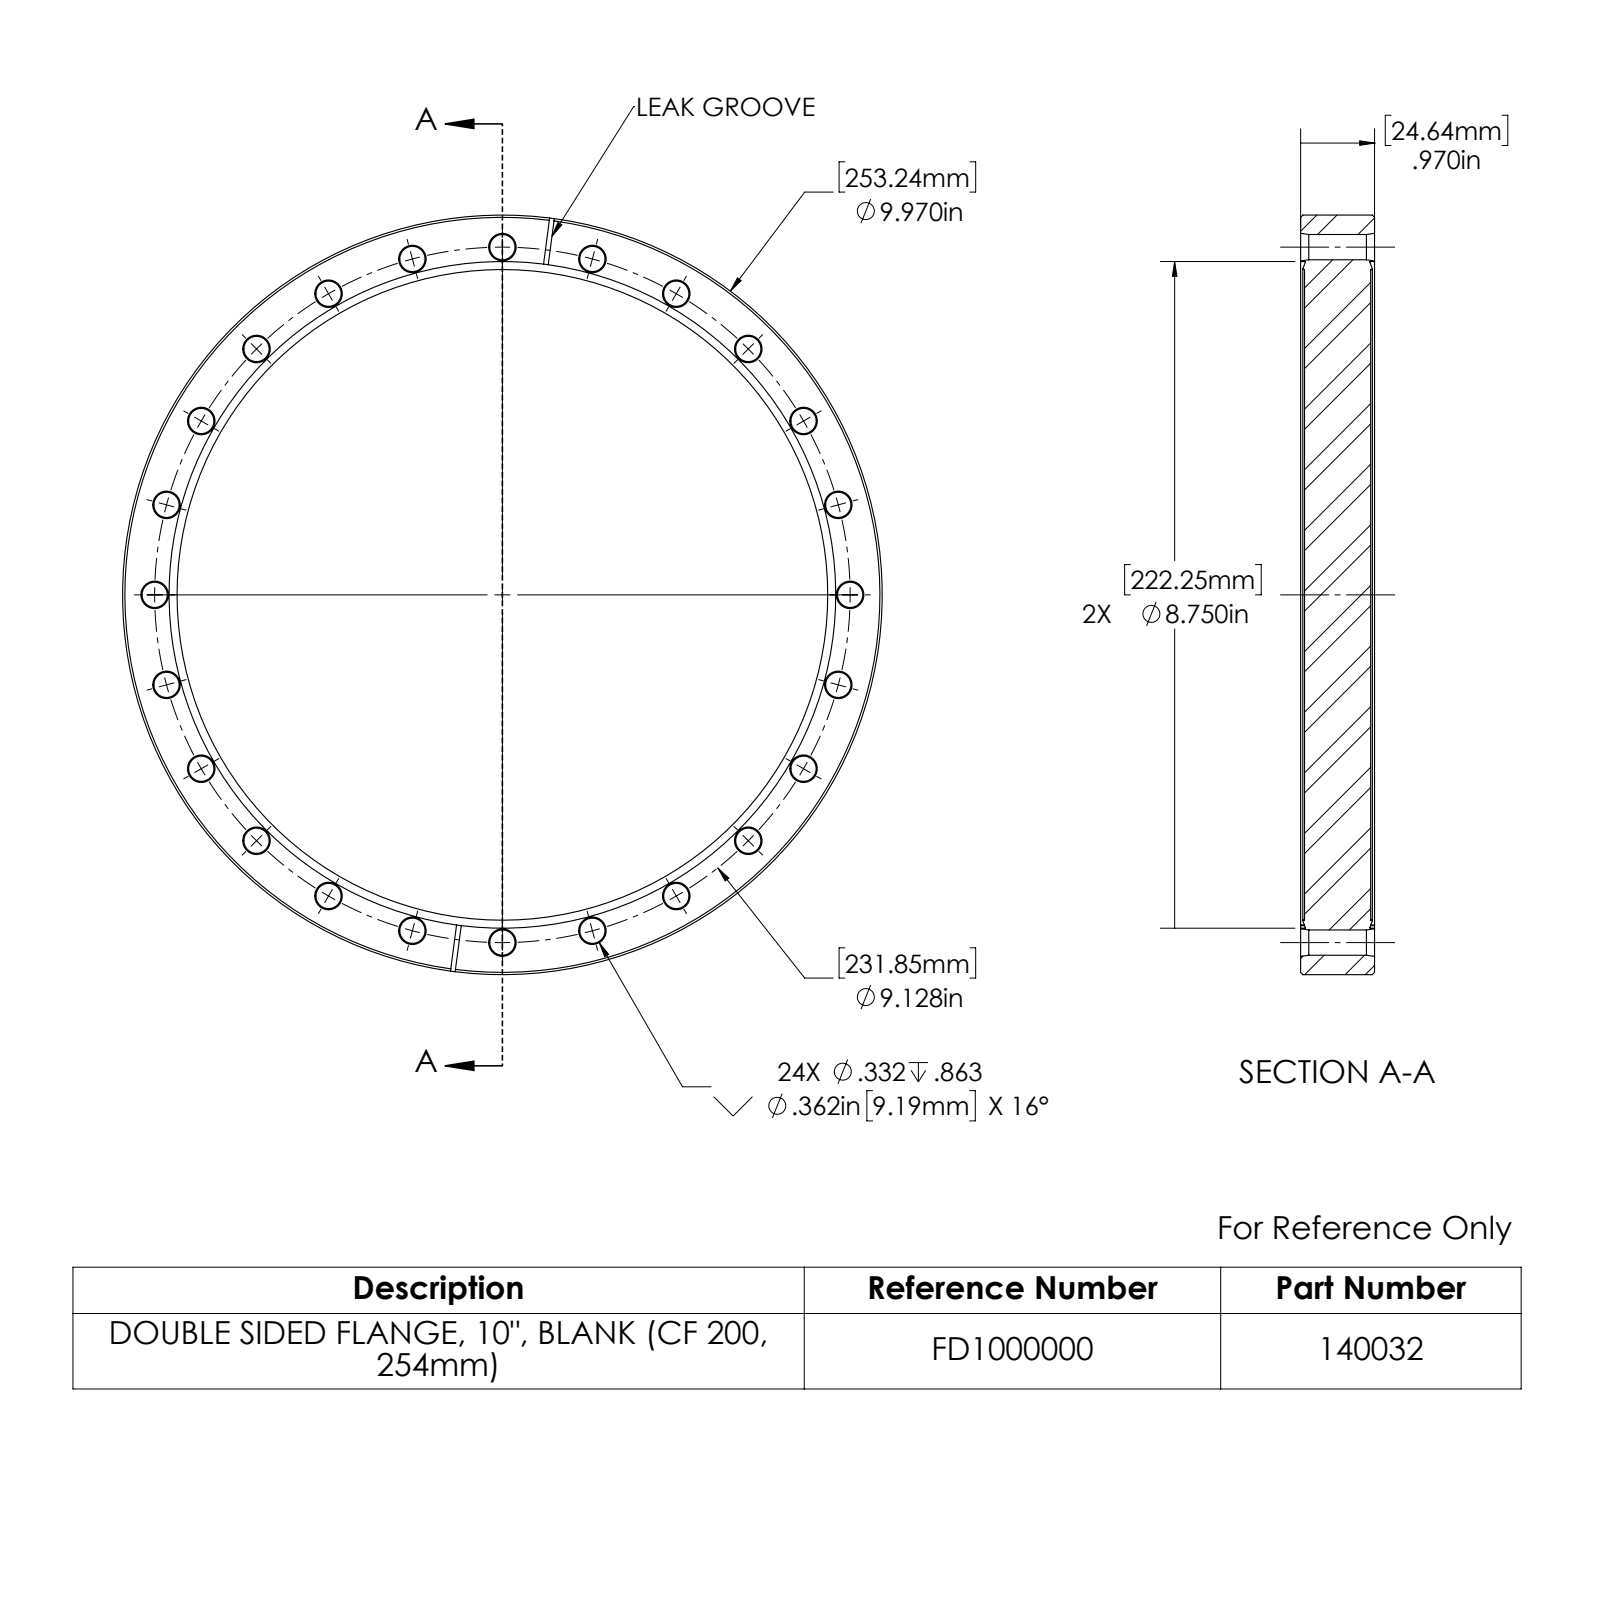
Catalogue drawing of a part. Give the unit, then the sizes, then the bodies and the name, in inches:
Units: inches
Overall size (bounding box): 9.97 × 9.97 × 0.97
Round holes (diameter × count): ⌀0.332 ×24, ⌀8.54 ×1, ⌀8.75 ×1
Round bosses / shafts (diameter × count): ⌀9.97 ×1
Partial cylindrical surfaces — rounded edges, fillets, slot ends (radius × count): R1.25 ×4
Main face-to-face distances: 0.868, 0.051, 0.919, 0.97, 0.062, 0.067, 0.057
Hole centre spacings: 4.564, 8.433, 2.363, 4.564, 7.905, 1.191, 3.493, 5.557
Volume: 67.52 in³ · Surface area: 210.2 in²
Bodies: 1 solid, 194 faces (14 planar, 62 cylindrical, 118 other)
Part name (STEP PRODUCT): 140032
STEP written by: SolidWorks 2022 (AUTOMOTIVE_DESIGN)
